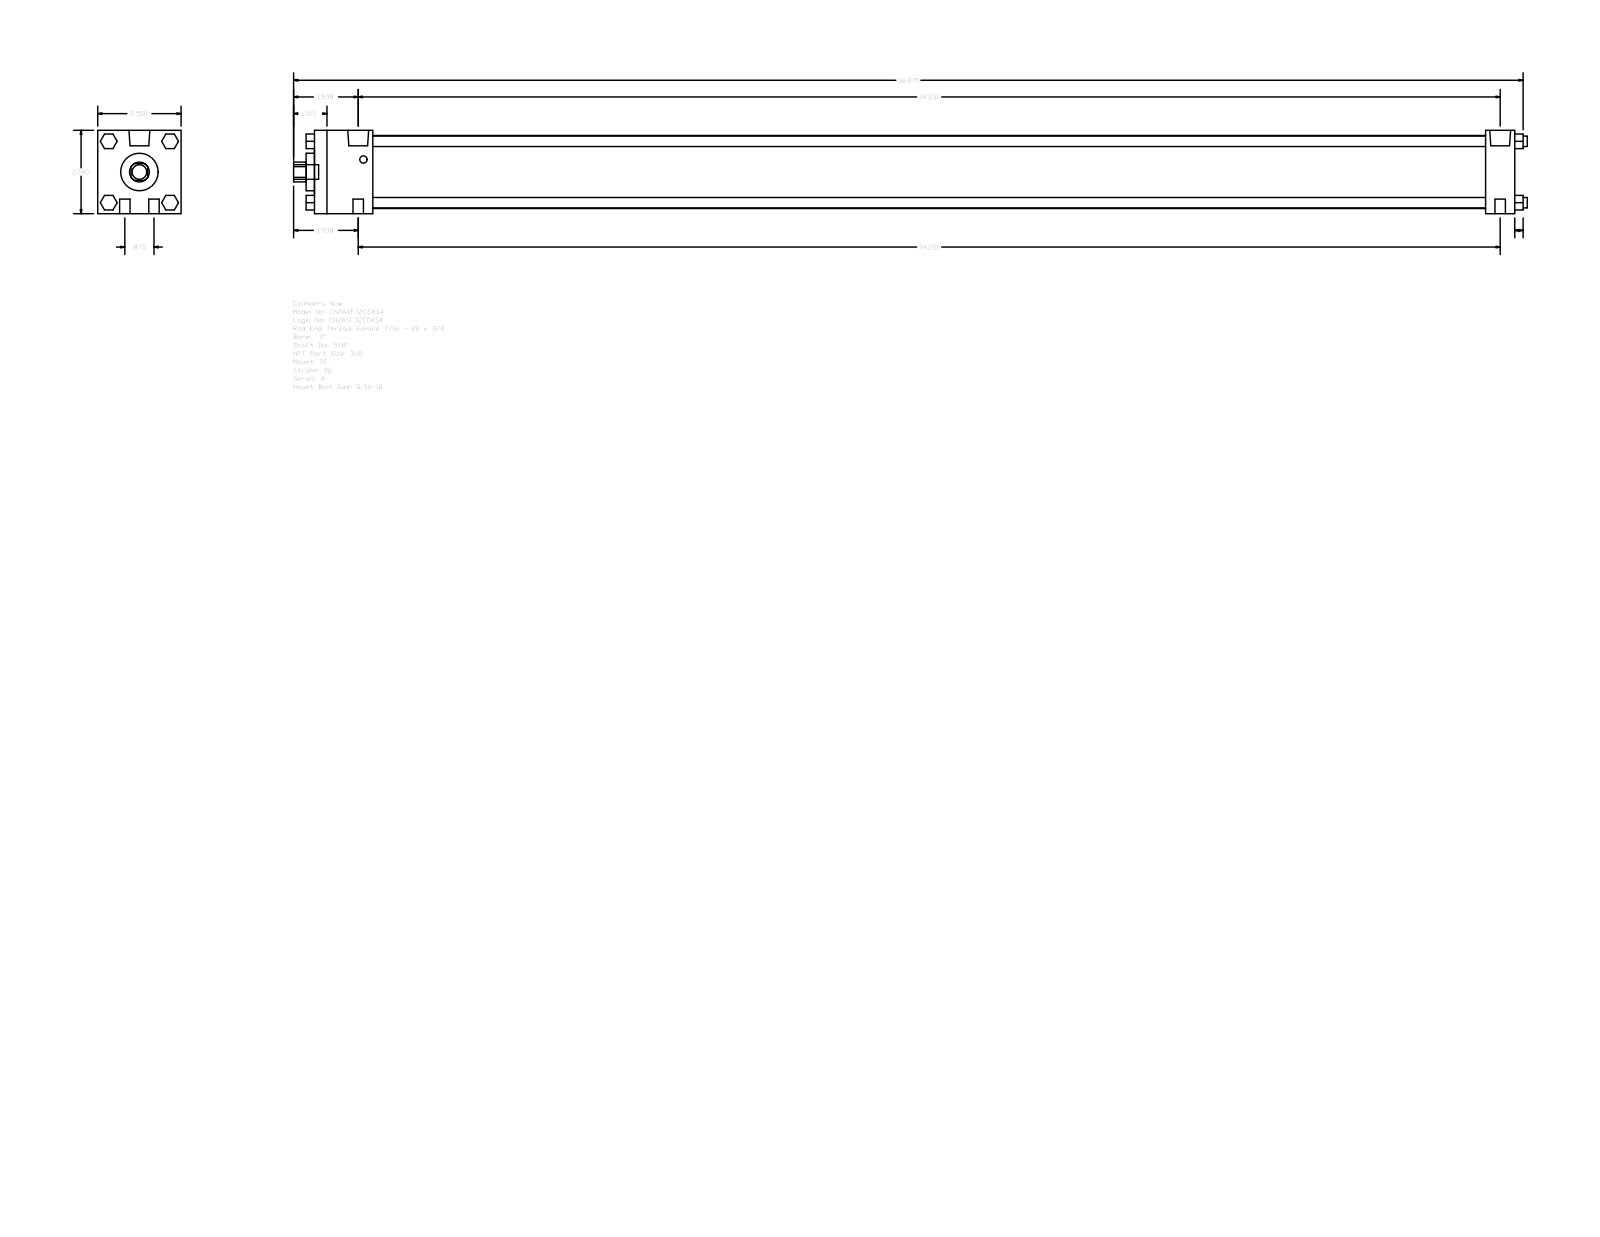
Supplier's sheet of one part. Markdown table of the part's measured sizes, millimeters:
| quantity | value |
| --- | --- |
| part name | A_SF__0200_0.625 |
| STEP written by | GSSL Pune (CONFIG_CONTROL_DESIGN) |
| units | millimeters |
| bodies | 0 solids, 124 faces (94 planar, 30 cylindrical, 0 other) |
| overall size | 939.8 × 63.5 × 63.5 |
| round holes (diameter × count) | 15.88 × 1, 28.57 × 1, 55.63 × 1 |
| round bosses / shafts (diameter × count) | 7.94 × 8, 15.93 × 2, 5.56 × 2, 11.11 × 1 |
| partial cylindrical surfaces (radius × count) | 7.54 × 1 |
| main face-to-face distances | 63.5, 914.39, 892.17, 22.22, 44.45, 847.72, 869.94, 6.35, 920.74, 50.8 |
